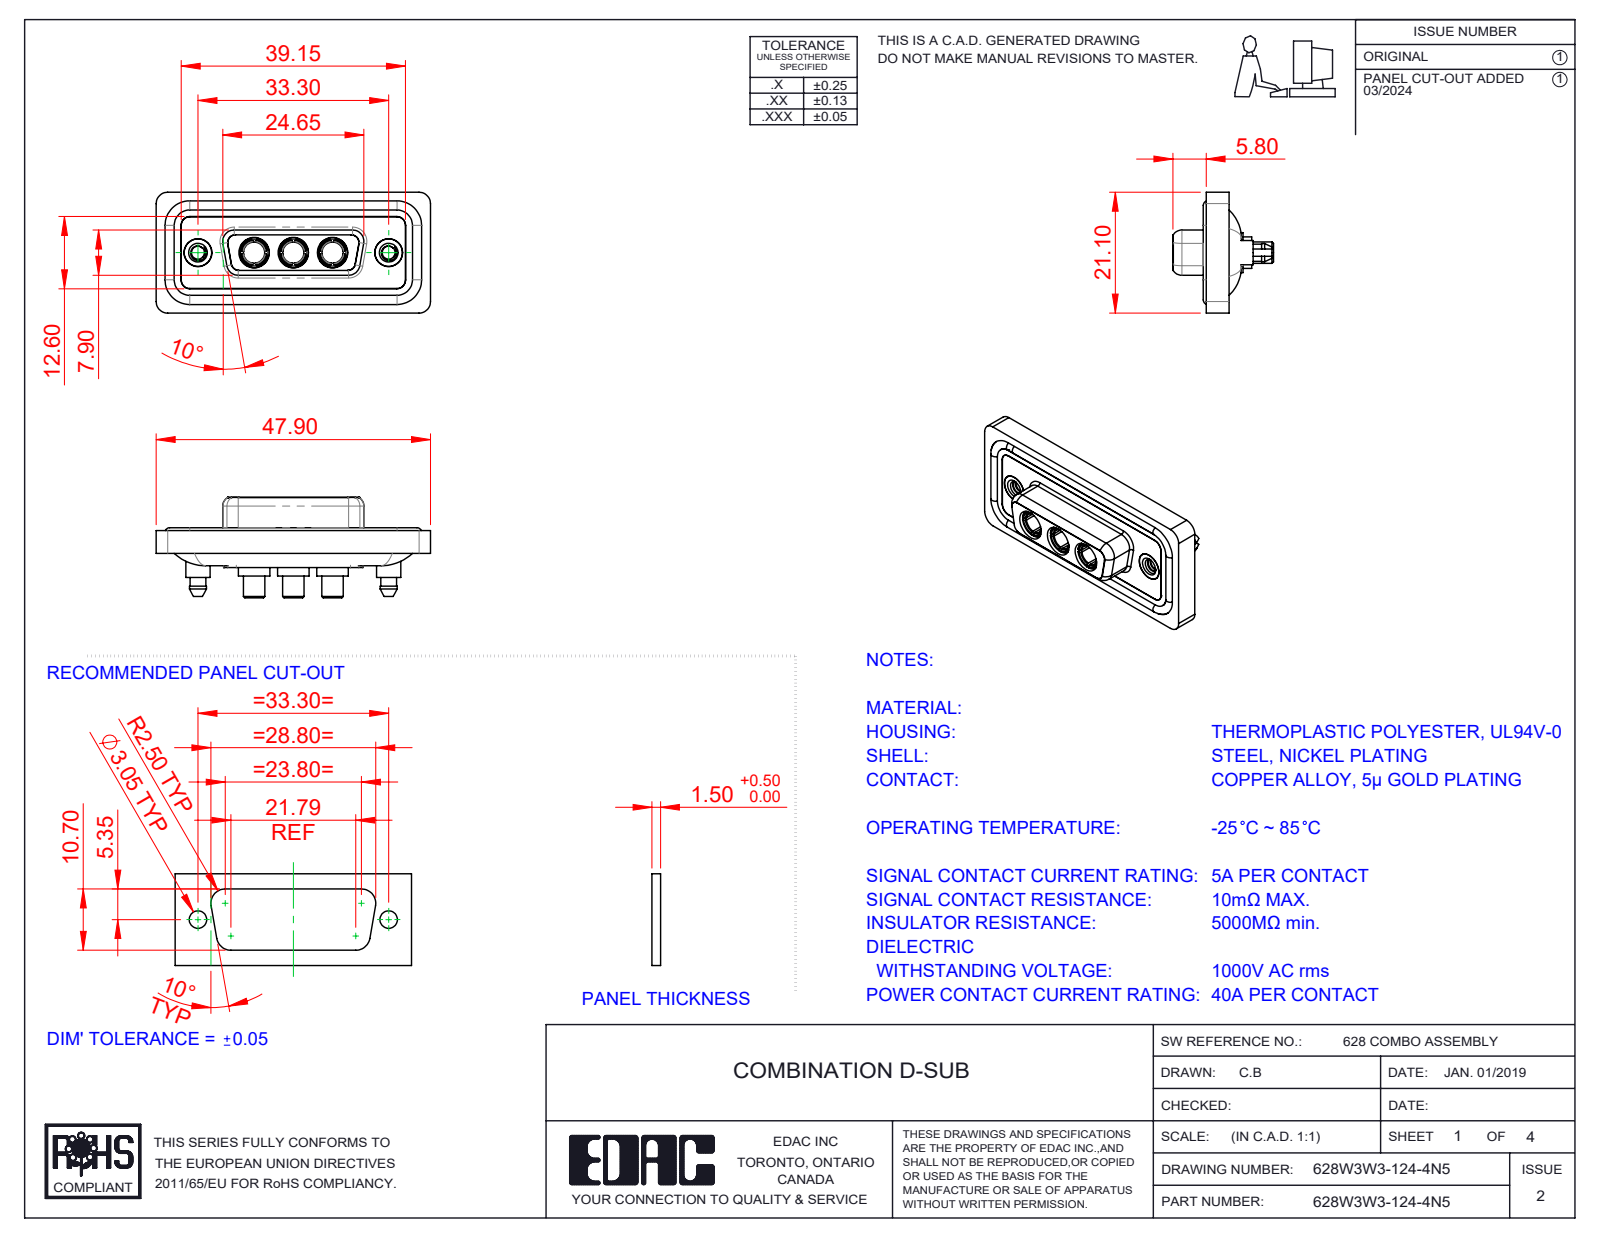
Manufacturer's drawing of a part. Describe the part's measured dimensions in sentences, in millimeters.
The part is named "628Combo Shell Front_15 Contacts; 628Combo Threaded Boardlock_5; 628Combo Waterproof Housing_15 Contacts; 628Combo Shell Rear_15 Contacts (+3 more)". Its 3-D file was written by "SolidWorks 2023 (CONFIG_CONTROL_DESIGN)". It is 13 solids with 658 faces: 208 planar, 289 cylindrical and 161 other. Overall it measures 47.9 by 21.1 by 17.55 millimeters. Its volume is 6 215 cubic millimeters and its surface area 10 104 square millimeters. Round holes: 5 of diameter 4.85, 3 of diameter 3.7, 3 of diameter 5.3, 2 of diameter 2.26, 2 of diameter 4, 2 of diameter 4.05, 2 of diameter 5. Round bosses or shafts: 4 of diameter 1.6, 3 of diameter 5.5, 3 of diameter 5.2, 3 of diameter 4.96, 3 of diameter 4.75, 3 of diameter 3.75, 2 of diameter 5.4, 2 of diameter 4.95. Partial cylindrical surfaces (rounded edges, fillets, slot ends): 24 of radius 1.5, 20 of radius 2, 12 of radius 1.35, 10 of radius 1.6, 4 of radius 0.25, 4 of radius 0.5, 4 of radius 0.6, 4 of radius 0.65. The main face-to-face distances are 0.4, 1.8, 1.6, 0.5, 7.45, 1.1, 2.9, 5.65, 7.05, 6.6. The hole center spacings are 6.85, 9.8, 16.65, 23.5, 13.7, 33.3.
